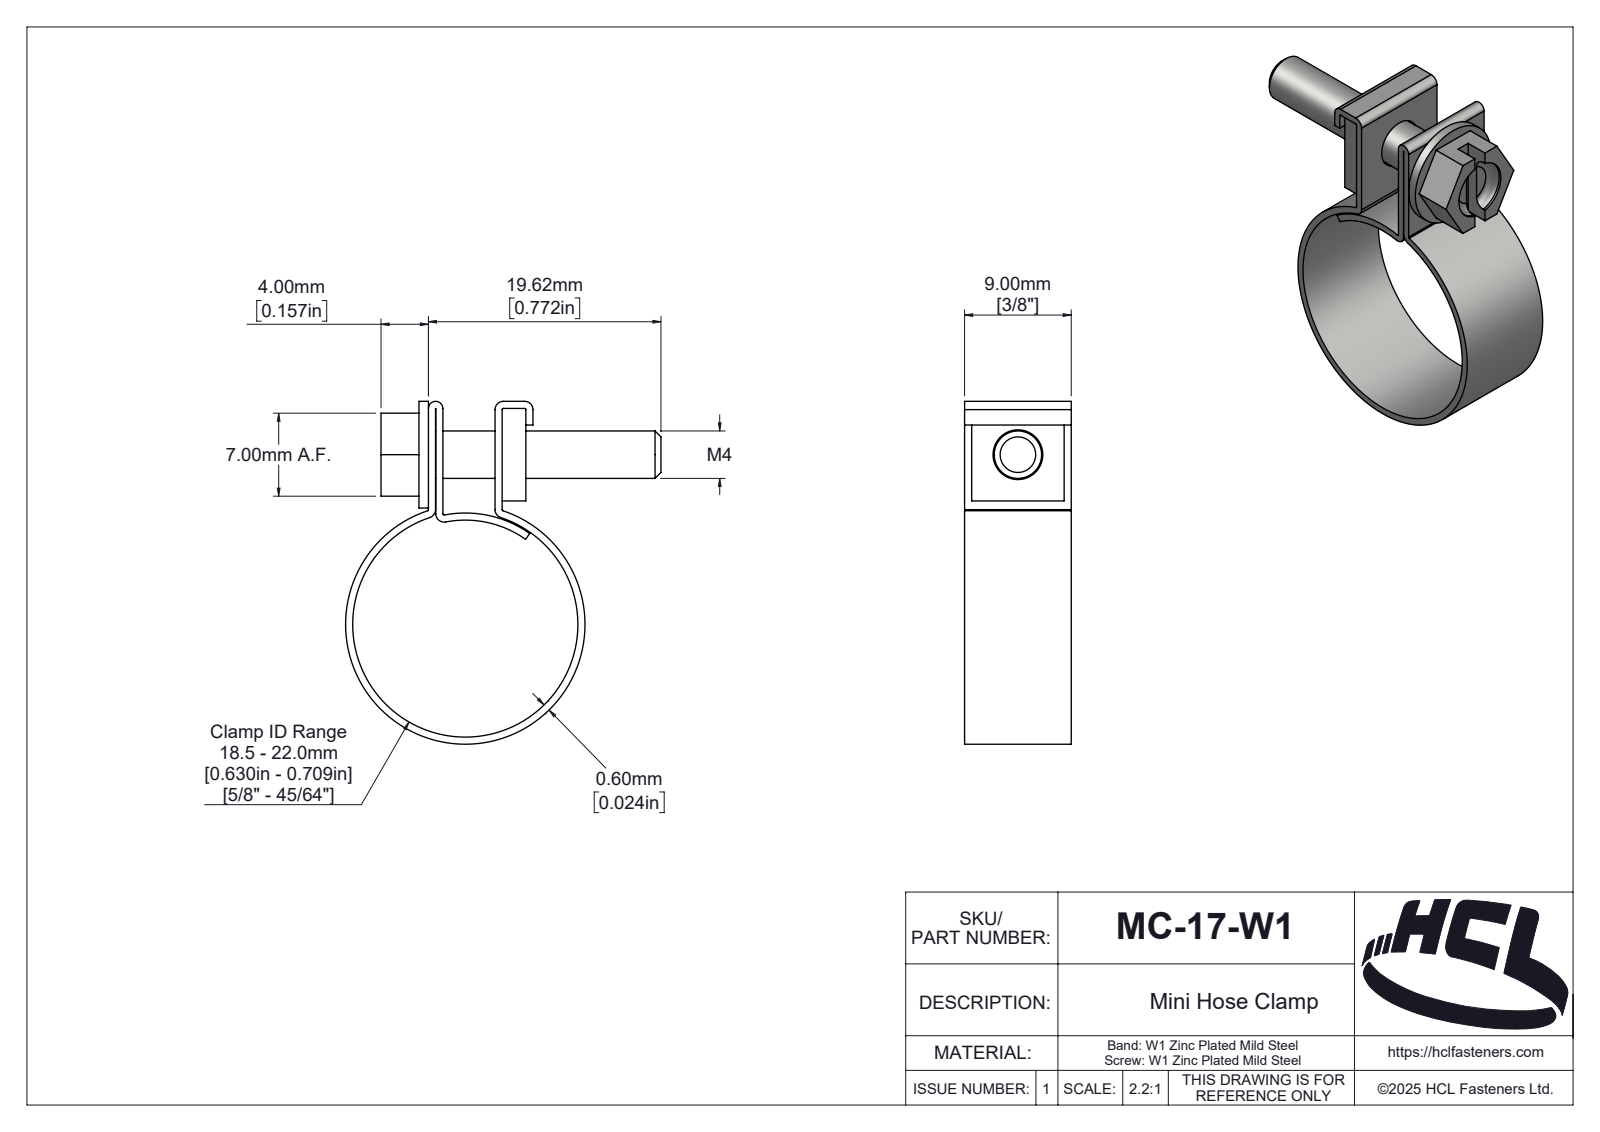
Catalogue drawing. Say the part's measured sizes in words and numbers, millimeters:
The part is named "MC-17-W1". Its 3-D file was written by "SolidWorks 2025 (AUTOMOTIVE_DESIGN)". It is 3 solids with 175 faces: 38 planar, 84 cylindrical and 53 other. Overall it measures 28.92 by 26.61 by 9 millimeters. Its volume is 987 cubic millimeters and its surface area 2 464 square millimeters. Round holes: 1 of diameter 4.2, 1 of diameter 5, 1 of diameter 19. Round bosses or shafts: 1 of diameter 20.2, 1 of diameter 9, 1 of diameter 4. Partial cylindrical surfaces (rounded edges, fillets, slot ends): 5 of radius 0.1, 5 of radius 0.7, 1 of radius 0.2, 1 of radius 0.61, 1 of radius 0.81, 1 of radius 1.01, 1 of radius 1.06, 1 of radius 1.28. The main face-to-face distances are 0.6, 0.62, 5, 5.62, 6.22, 7, 2, 2.6, 8.22, 7.6.
